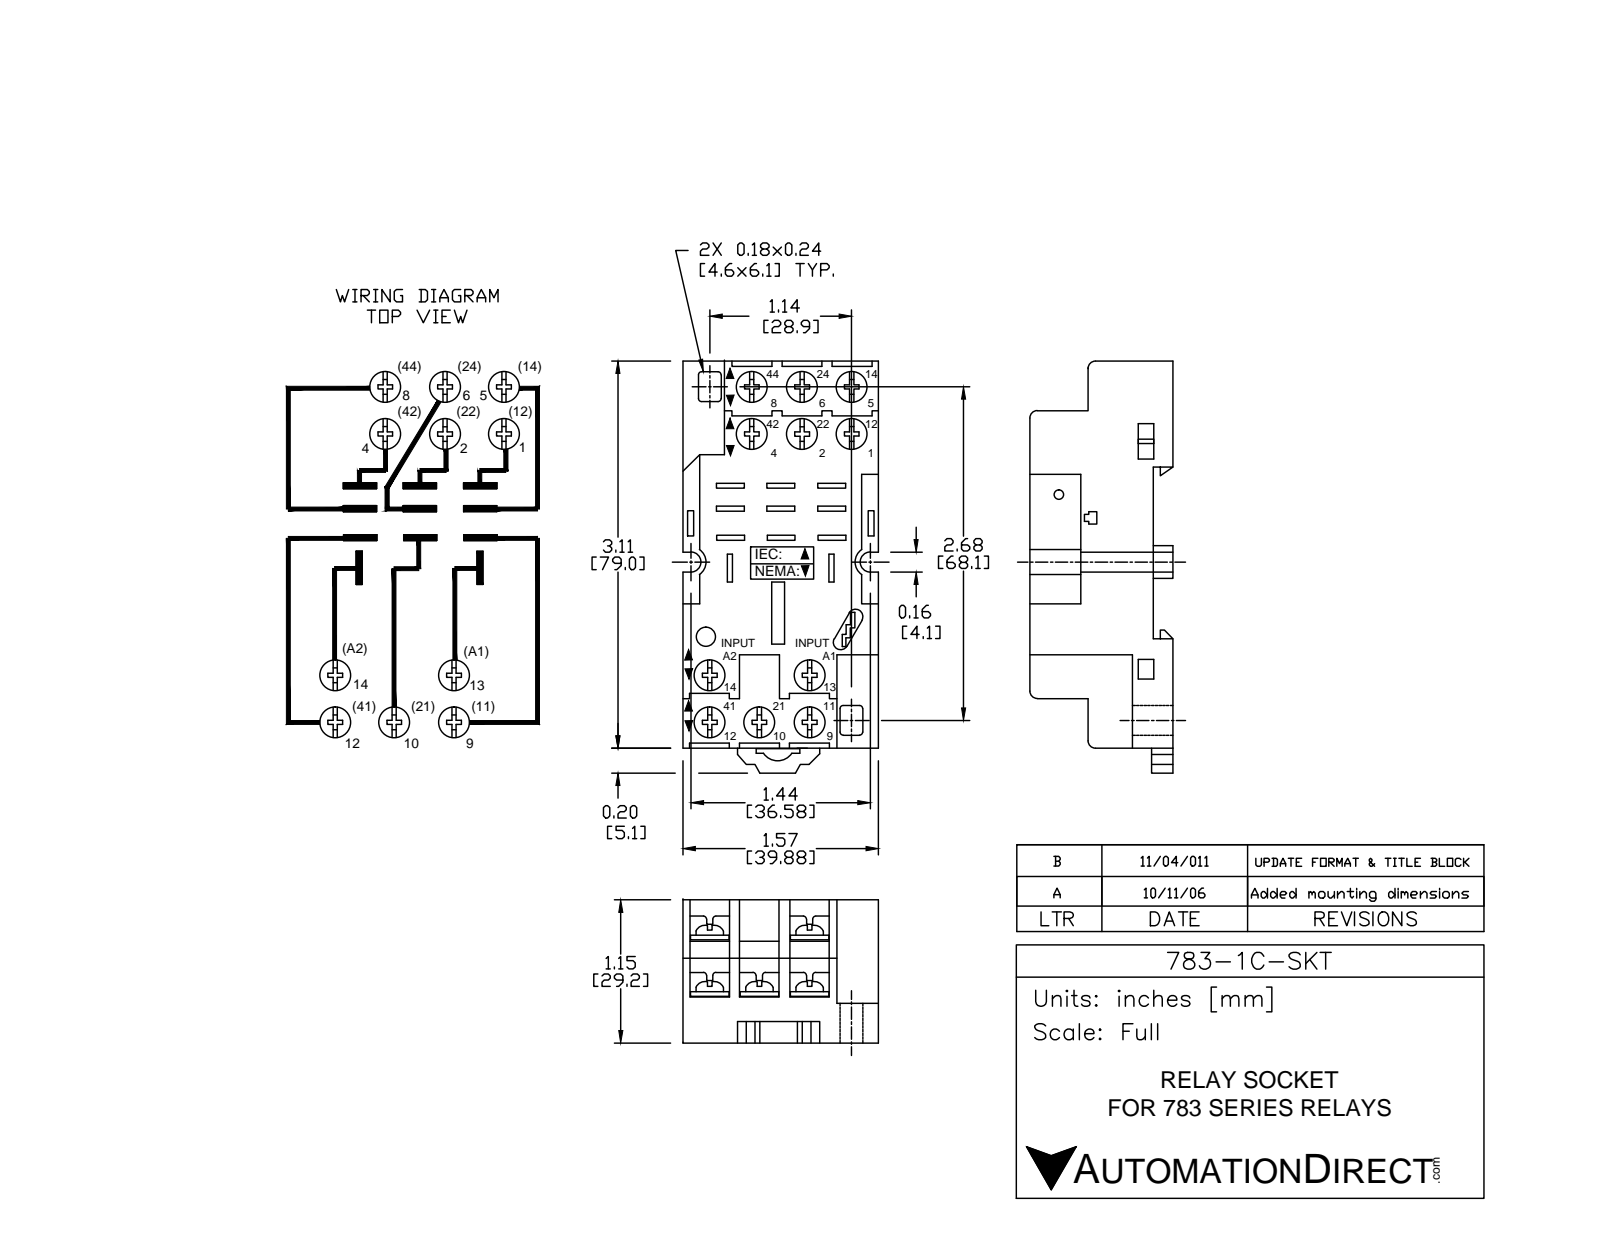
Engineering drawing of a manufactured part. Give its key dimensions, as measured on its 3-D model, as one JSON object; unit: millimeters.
{"part_name": "783-3C-SKT", "step_written_by": "SolidWorks 2013 (AUTOMOTIVE_DESIGN)", "units": "millimeters", "bodies": {"solids": 1, "faces": 479, "planar": 378, "cylindrical": 101, "other": 0}, "overall_size": [84.1, 39.9, 29.2], "volume_mm3": 64470, "surface_area_mm2": 16930, "round_holes": [[5.3, 11], [3.2, 1]], "partial_cylinders_radius": [[0.4, 44], [0.8, 8], [1.5, 6], [2, 2], [3, 2], [3.4, 1]], "face_to_face_distances": [4.3, 29.2, 24.9, 39.9, 8.4, 3.3, 11.9, 31.5, 28.2, 8.9], "hole_center_spacings": [10.2, 14.2, 59.8, 59.2, 9.9, 9.9, 19.8, 19.8]}
